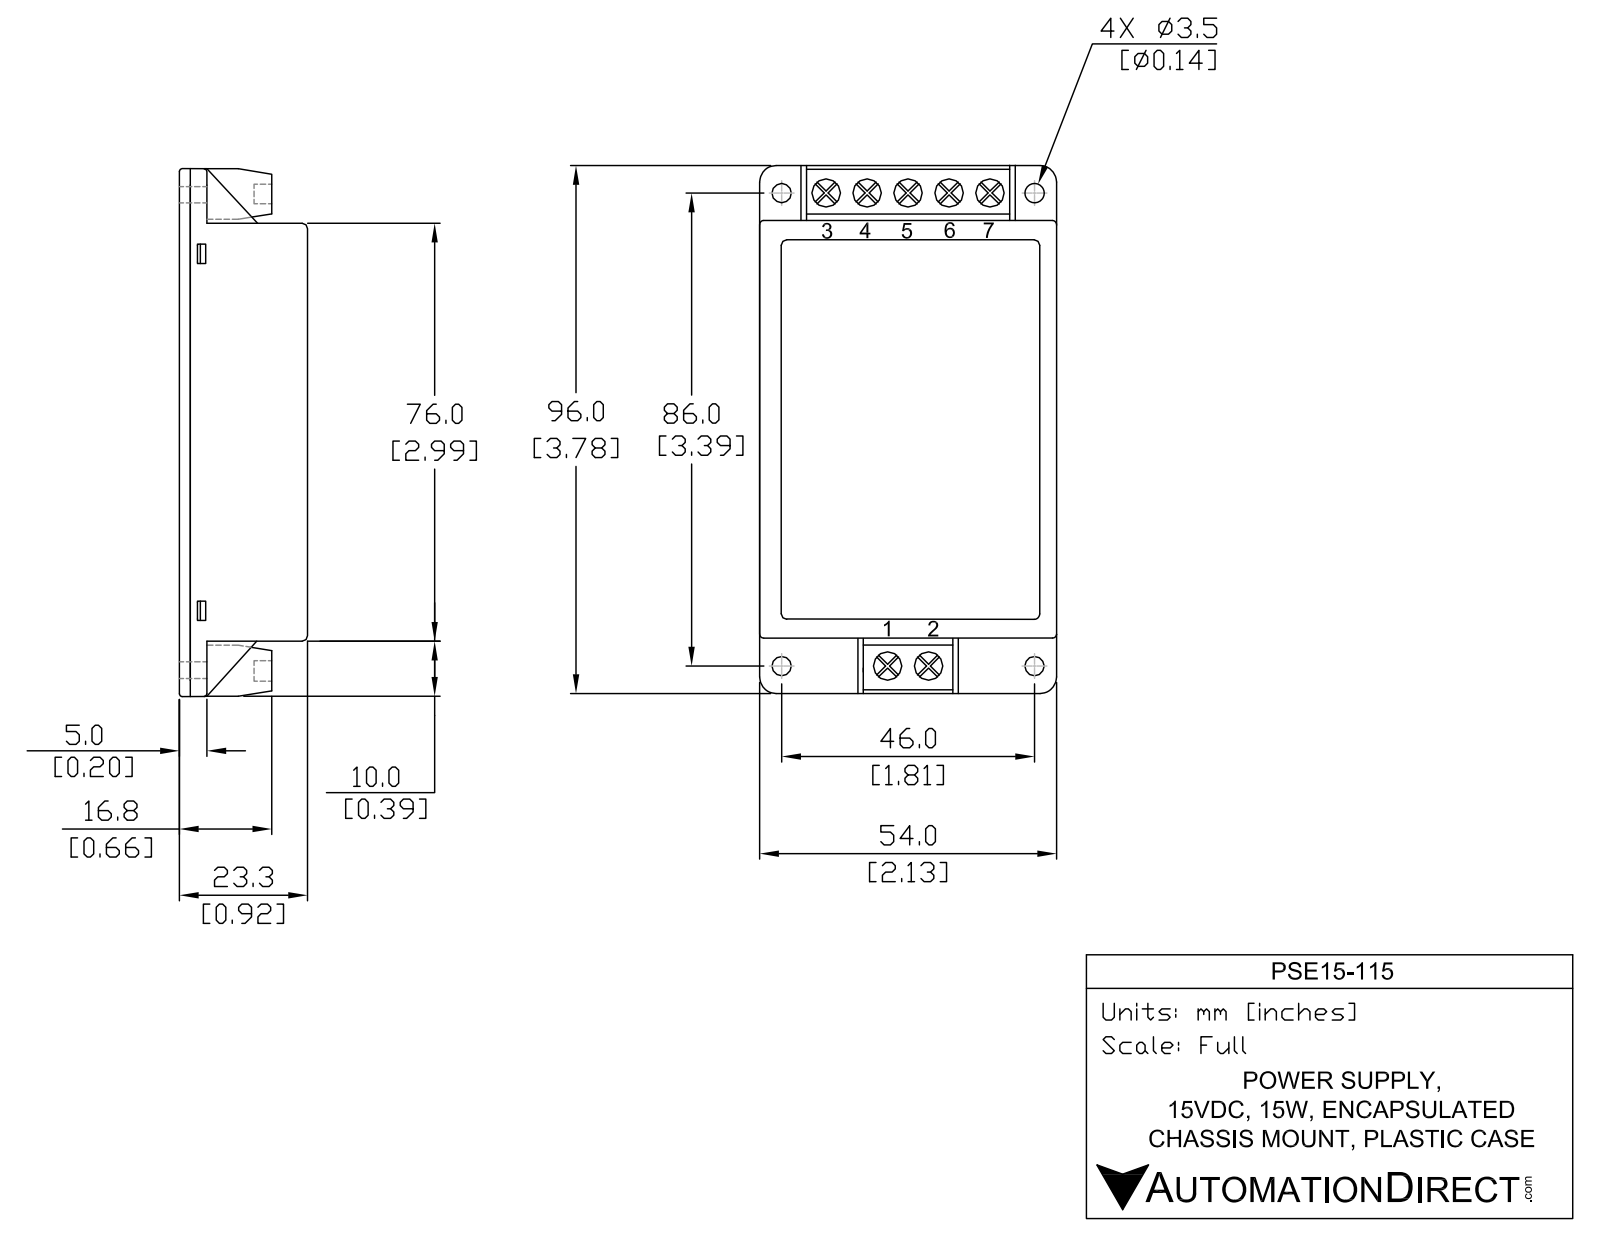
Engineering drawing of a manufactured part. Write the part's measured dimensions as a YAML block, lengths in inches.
part_name: "PSE15-115"
step_written_by: "SolidWorks 2011 (CONFIG_CONTROL_DESIGN)"
units: inches
bodies: {solids: 2, faces: 369, planar: 246, cylindrical: 62, other: 61}
overall_size: [3.78, 2.13, 0.92]
volume: 6.464
surface_area: 45.54
round_holes:
  - {diameter: 0.2, count: 7}
  - {diameter: 0.14, count: 4}
partial_cylinders:
  - {radius: 0.03, count: 20}
  - {radius: 0.125, count: 4}
face_to_face_distances: [0.078, 0.08, 0.84, 0.918, 0.838, 2.13, 2.99, 0.92, 0.842, 0.015]
hole_center_spacings: [0.26, 0.52, 0.26, 0.775, 1.035, 1.81, 3.362, 3.363]
